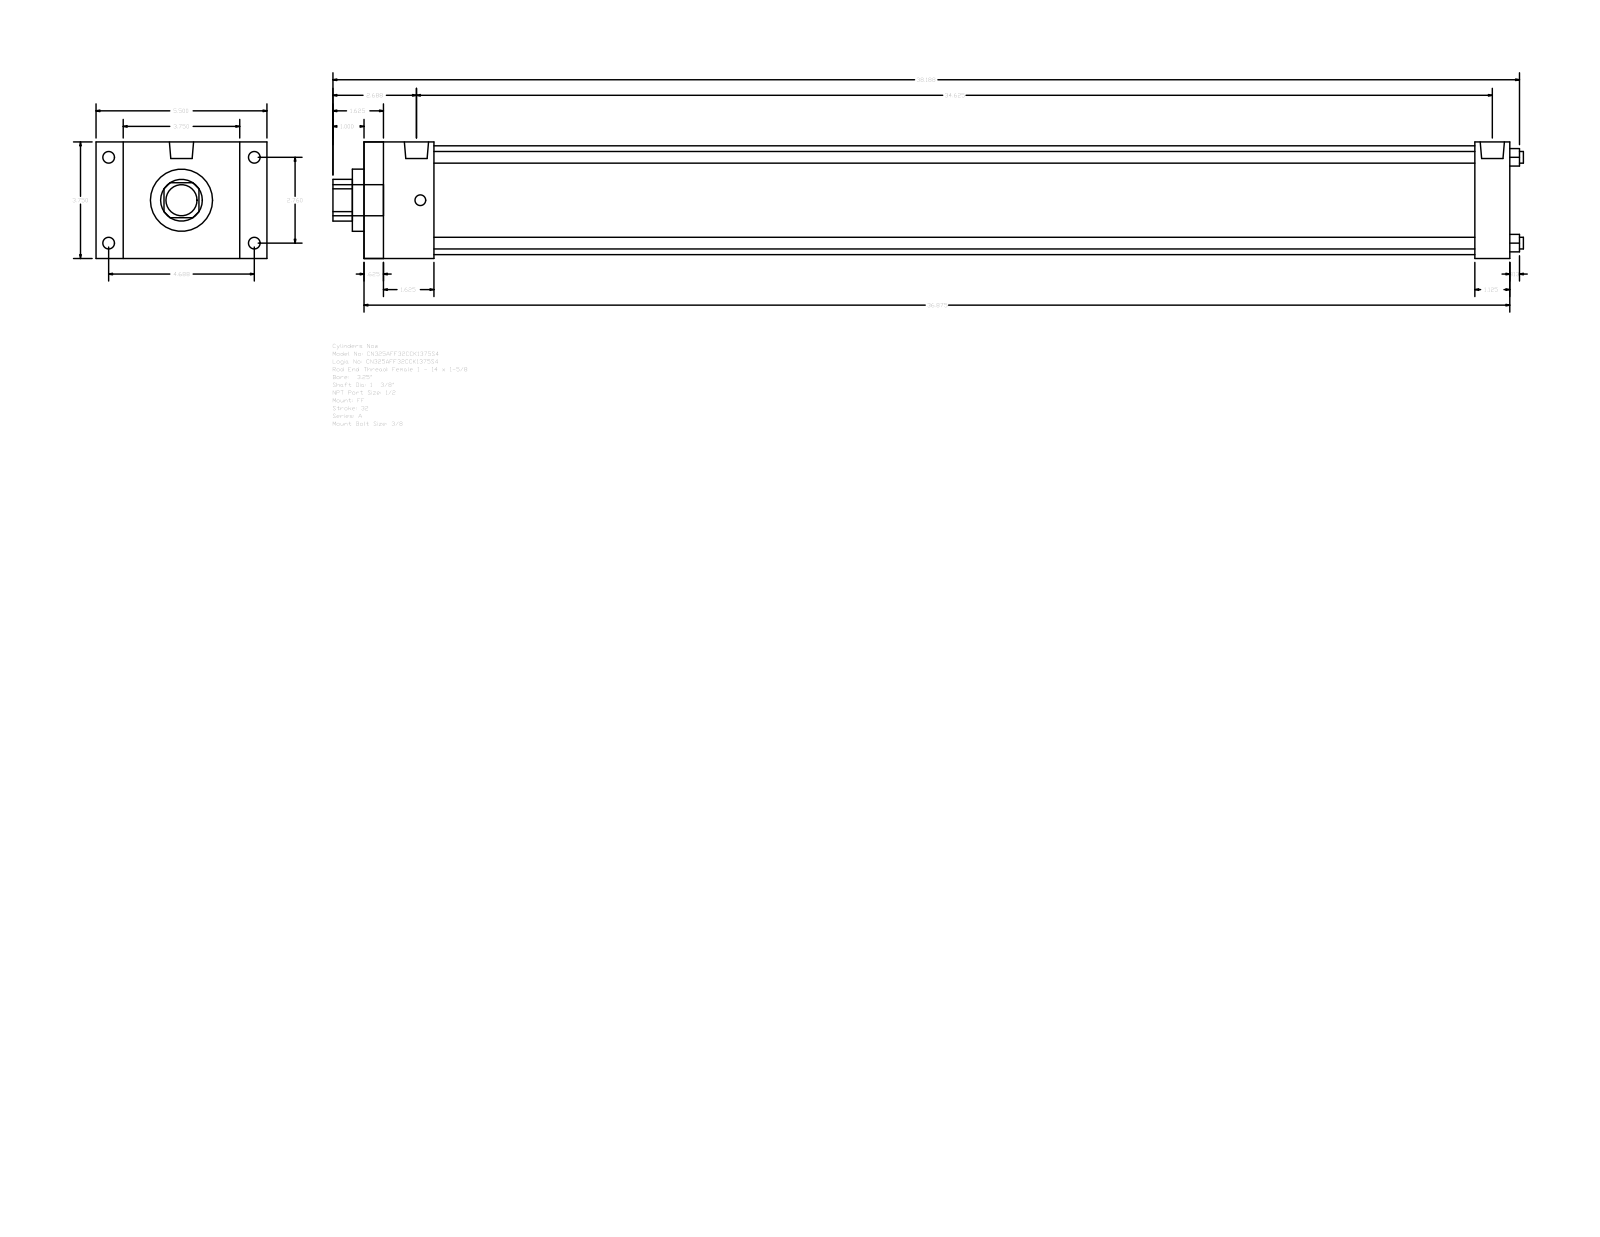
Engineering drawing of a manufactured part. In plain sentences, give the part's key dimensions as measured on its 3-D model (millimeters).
The part is named "A_FF__0325_1.375". Its 3-D file was written by "GSSL Pune (CONFIG_CONTROL_DESIGN)". It is 0 solids with 92 faces: 64 planar, 28 cylindrical and 0 other. Overall it measures 973.14 by 139.7 by 95.25 millimeters. Round holes: 4 of diameter 9.53, 1 of diameter 34.92, 1 of diameter 50.8, 1 of diameter 88.9. Round bosses or shafts: 4 of diameter 9.53, 4 of diameter 8.73, 2 of diameter 19.77, 1 of diameter 25.4. Partial cylindrical surfaces (rounded edges, fillets, slot ends): 1 of radius 17.06. The main face-to-face distances are 95.24, 936.62, 920.75, 15.87, 22.23, 117.47, 28.57, 57.15, 908.05, 41.28. The hole center spacings are 49.57, 70.1, 99.14.
